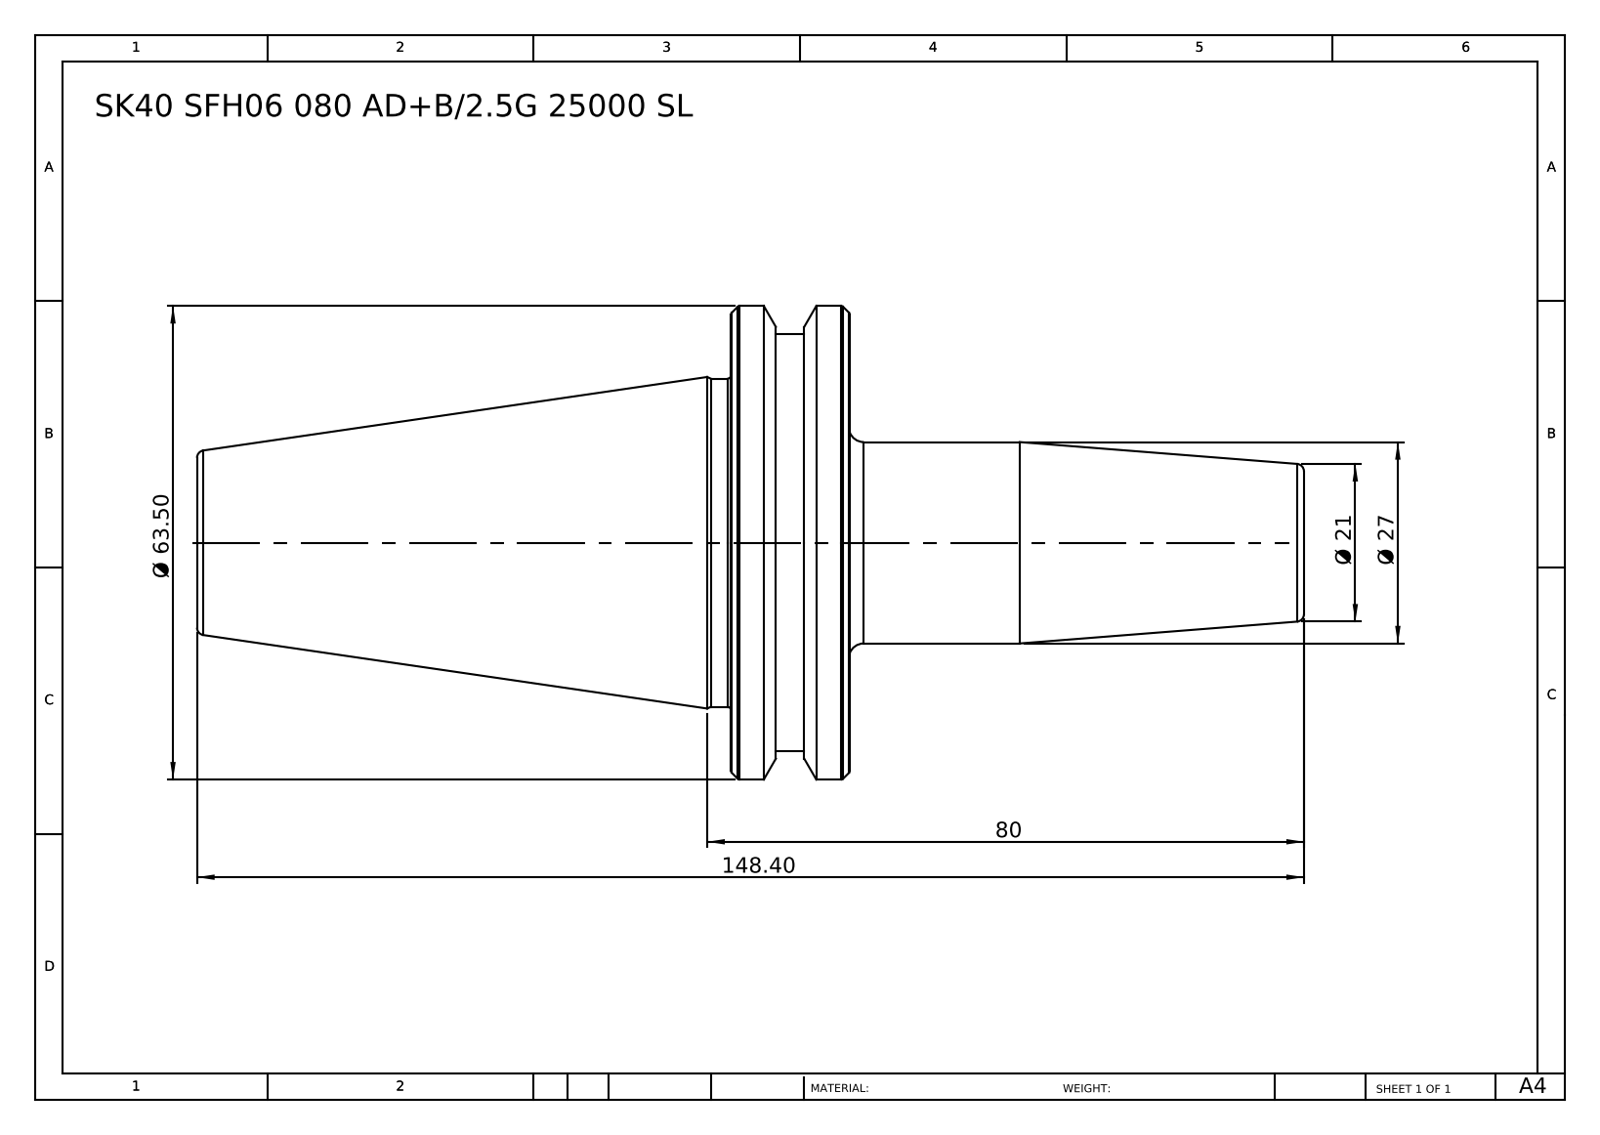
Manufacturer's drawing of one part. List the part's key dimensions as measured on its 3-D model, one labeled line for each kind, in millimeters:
Part name (STEP PRODUCT): SK40 SFH06 80 AD+B-2.5G 25000 SL
STEP written by: SolidWorks 2014 (CONFIG_CONTROL_DESIGN)
Units: millimetres
Bodies: 1 solid, 46 faces (6 planar, 10 cylindrical, 30 other)
Overall size (bounding box): 148.4 × 63.5 × 63.5
Volume: 147 522 mm³ · Surface area: 21 429 mm²
Round bosses / shafts (diameter × count): ⌀63.5 ×1, ⌀56 ×1, ⌀44 ×1, ⌀27 ×1
Main face-to-face distances: 15.9, 87.5, 71.6, 60.9, 76.8, 148.4, 67, 6.1, 9.8, 81.4
